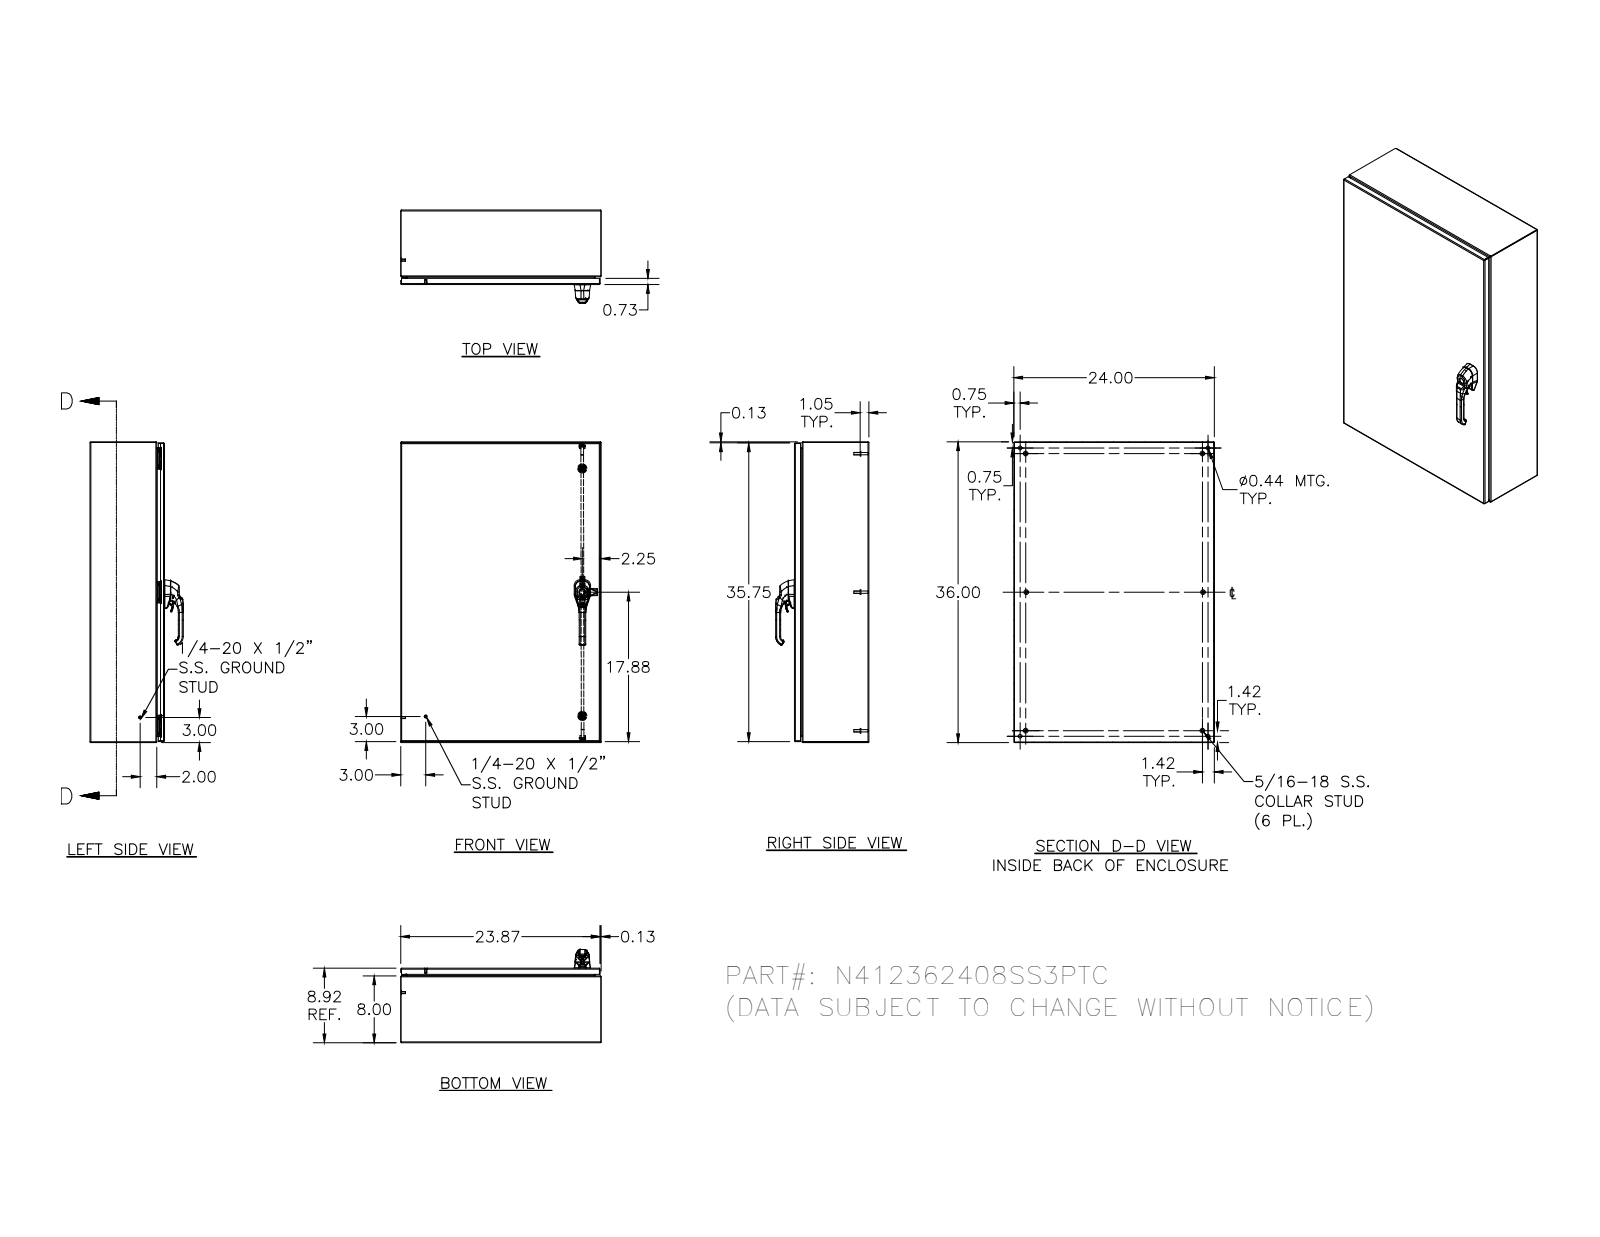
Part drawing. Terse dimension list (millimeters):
name: N412362408SS3PTC; N412362408SS3PTCBKP; N4123624SS3PTCLID; HFW328176 (+8 more)
written by: Autodesk Inventor 2011 (AUTOMOTIVE_DESIGN)
unit: mm
bodies: 74 solids, 3522 faces (1171 planar, 1295 cylindrical, 1056 other)
size: 914.4 × 609.6 × 283.6
volume: 3 744 000 mm³; area: 3 902 000 mm²
holes: 6× ⌀2.4, 6× ⌀3.9, 6× ⌀4.2, 6× ⌀4.4, 6× ⌀4.8, 5× ⌀4.2, 4× ⌀5, 4× ⌀11.1, 3× ⌀4, 3× ⌀5.4, 2× ⌀2.7, 2× ⌀4.1
bosses: 14× ⌀6.4, 6× ⌀14.3, 6× ⌀9.1, 6× ⌀8.1, 6× ⌀7.6, 6× ⌀7, 6× ⌀6.5, 6× ⌀6
rounds: 178× R0.5, 101× R0.3, 38× R1.3, 34× R0.8, 26× R0.4, 23× R3, 21× R0.5, 21× R3.2
face distances: 1.9, 224.6, 222.7, 226.5, 607.7, 912.5, 605.8, 609.6, 914.4, 910.6
hole spacings: 406.4, 406.3, 812.7, 406.6, 0.4, 16.8, 423.1, 580.9
